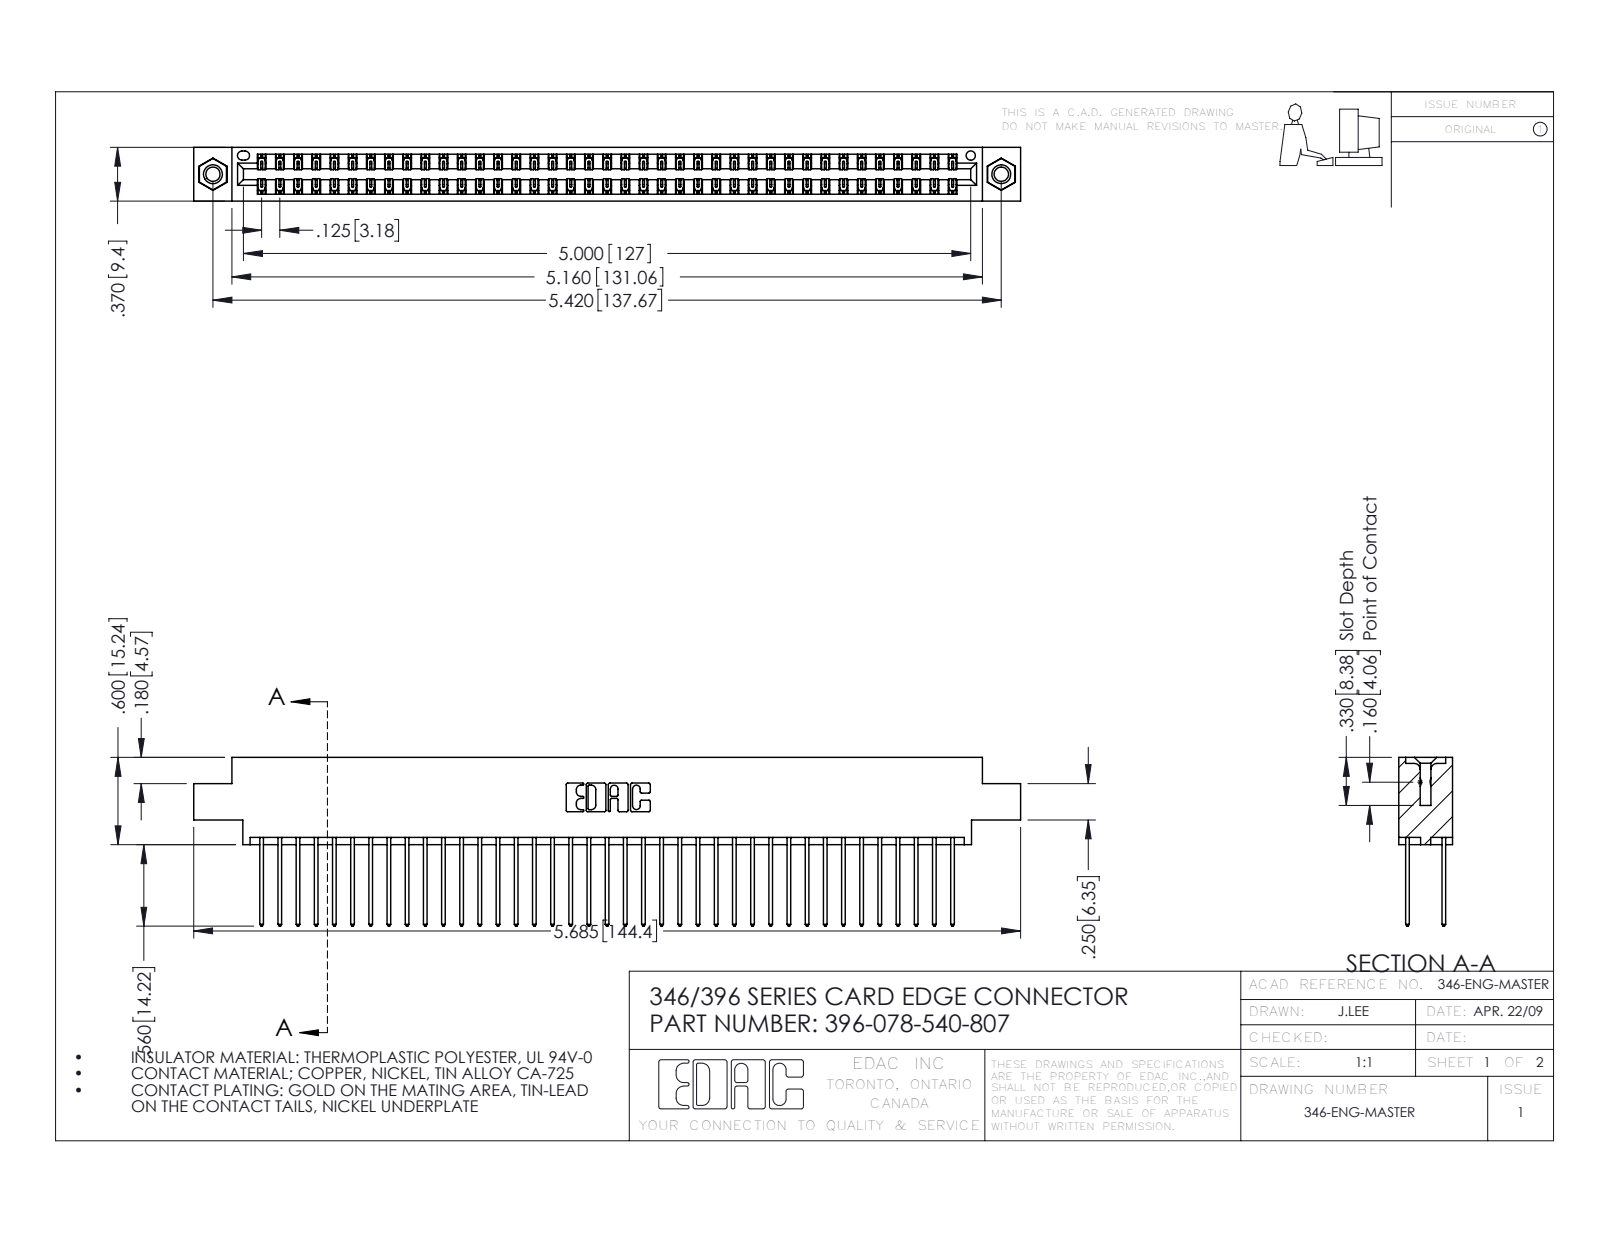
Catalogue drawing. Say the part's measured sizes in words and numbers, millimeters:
The part is named "345-250-001_345-250-005-103; 396-078-540-807; 346 Part_0.170 Offset - 0.156 Dia-TI; 345-292-001_345-293-140". Its 3-D file was written by "SolidWorks 2016 (CONFIG_CONTROL_DESIGN)". It is 81 solids with 4242 faces: 2842 planar, 1384 cylindrical and 16 other. Overall it measures 144.4 by 29.5 by 9.4 millimeters. Its volume is 14 200 cubic millimeters and its surface area 21 060 square millimeters. Round holes: 2 of diameter 2.5, 2 of diameter 3.2, 2 of diameter 4, 1 of diameter 1.6. Round bosses or shafts: 2 of diameter 3.9. Partial cylindrical surfaces (rounded edges, fillets, slot ends): 117 of radius 0.2, 78 of radius 0.3, 22 of radius 0.3, 6 of radius 0.2, 6 of radius 0.8, 3 of radius 0.7, 2 of radius 0.4, 2 of radius 0.6. The main face-to-face distances are 1.2, 8.2, 6.4, 1.8, 7.6, 0.6, 9.4, 7, 5.6, 3.8. The hole center spacings are 6.2, 132.4, 137.7.
